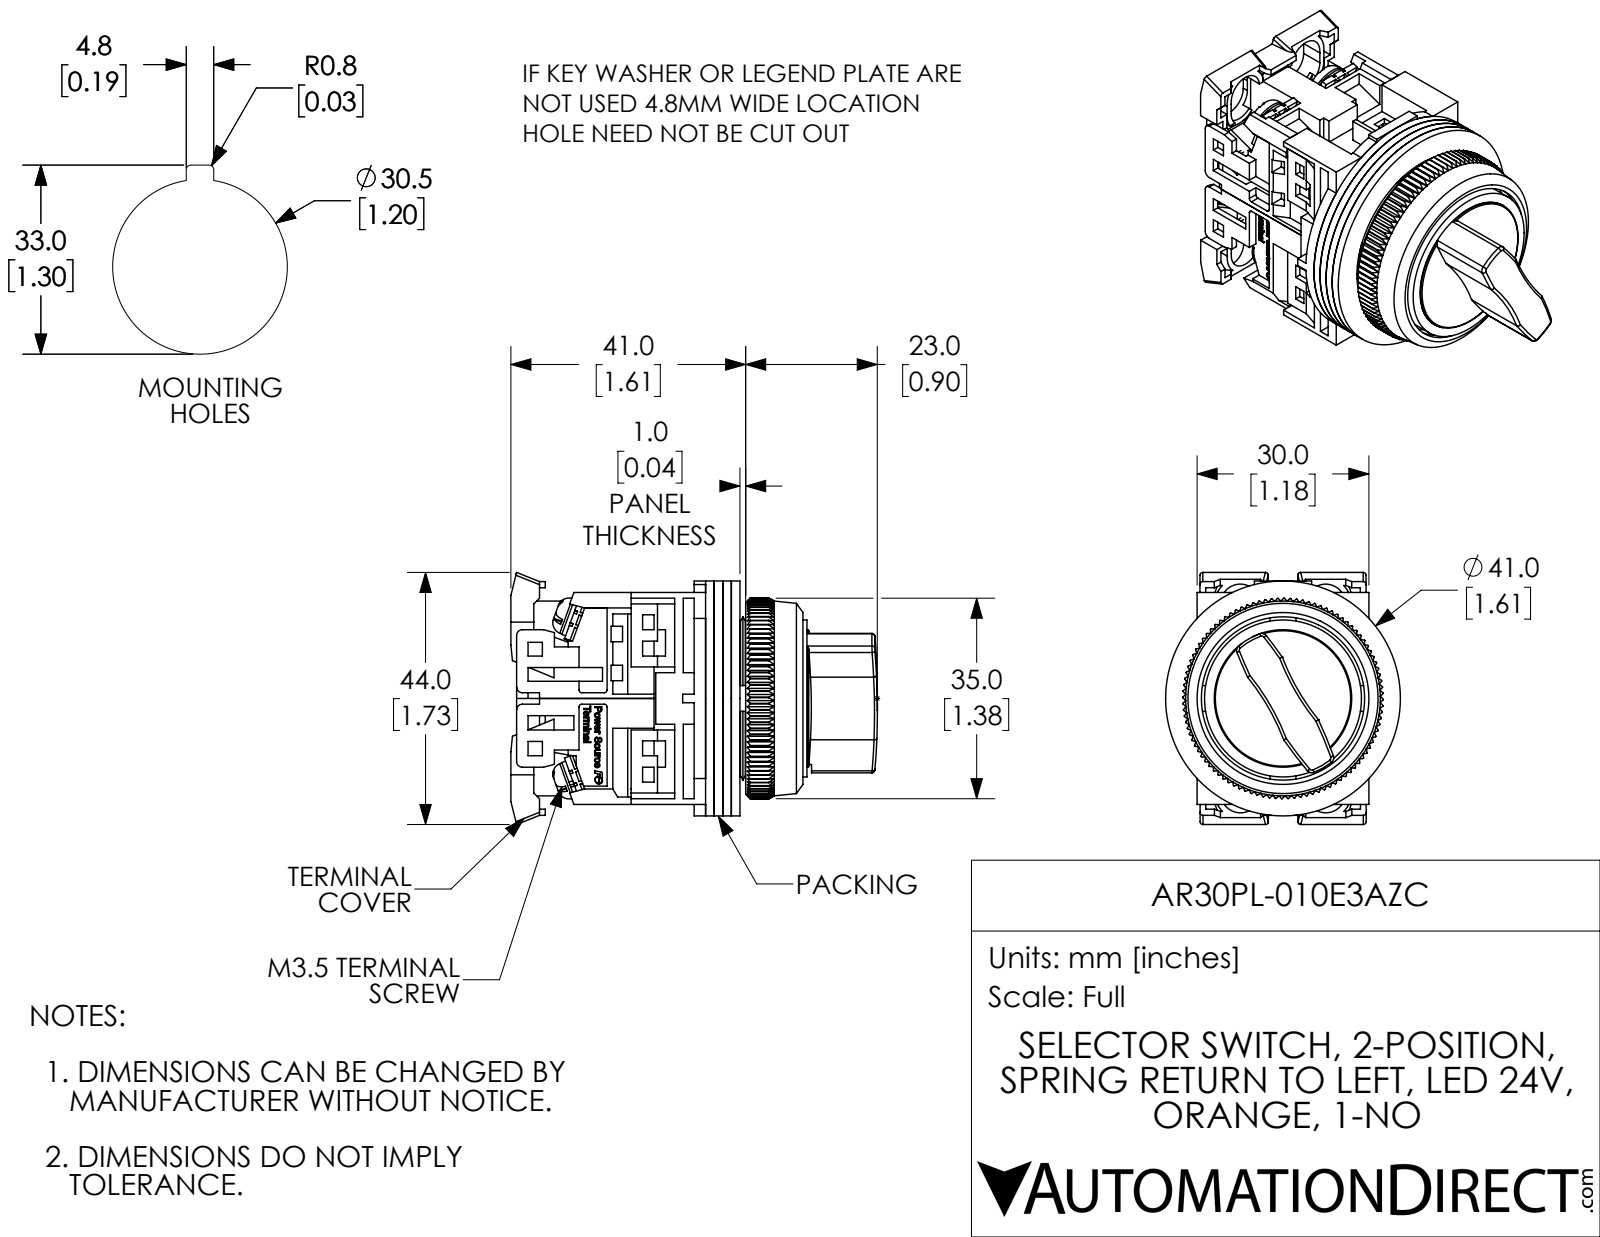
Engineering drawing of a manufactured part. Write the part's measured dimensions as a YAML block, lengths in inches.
part_name: "AR30PL-010E3AZC"
step_written_by: "SolidWorks 2017 (AUTOMOTIVE_DESIGN)"
units: inches
bodies: {solids: 25, faces: 2434, planar: 1731, cylindrical: 305, other: 398}
overall_size: [2.52, 1.732, 1.614]
volume: 2.238
surface_area: 59.31
round_holes:
  - {diameter: 0.138, count: 8}
  - {diameter: 0.142, count: 4}
  - {diameter: 0.118, count: 1}
  - {diameter: 0.472, count: 1}
  - {diameter: 0.709, count: 1}
  - {diameter: 0.768, count: 1}
  - {diameter: 0.827, count: 1}
  - {diameter: 1.122, count: 1}
  - {diameter: 1.181, count: 1}
  - {diameter: 1.252, count: 1}
round_bosses_or_shafts:
  - {diameter: 0.26, count: 4}
  - {diameter: 0.138, count: 4}
  - {diameter: 0.063, count: 2}
  - {diameter: 1.614, count: 1}
  - {diameter: 1.15, count: 1}
  - {diameter: 1.079, count: 1}
  - {diameter: 0.945, count: 1}
  - {diameter: 0.886, count: 1}
partial_cylinders:
  - {radius: 0.059, count: 16}
  - {radius: 0.02, count: 12}
  - {radius: 0.039, count: 8}
  - {radius: 0.138, count: 4}
  - {radius: 0.177, count: 4}
  - {radius: 0.118, count: 2}
  - {radius: 1.575, count: 2}
  - {radius: 2.953, count: 2}
face_to_face_distances: [0.059, 0.118, 0.177, 0.039, 0.079, 1.417, 1.358, 0.811, 0.197, 0.02]
hole_center_spacings: [0.579, 0.61]
